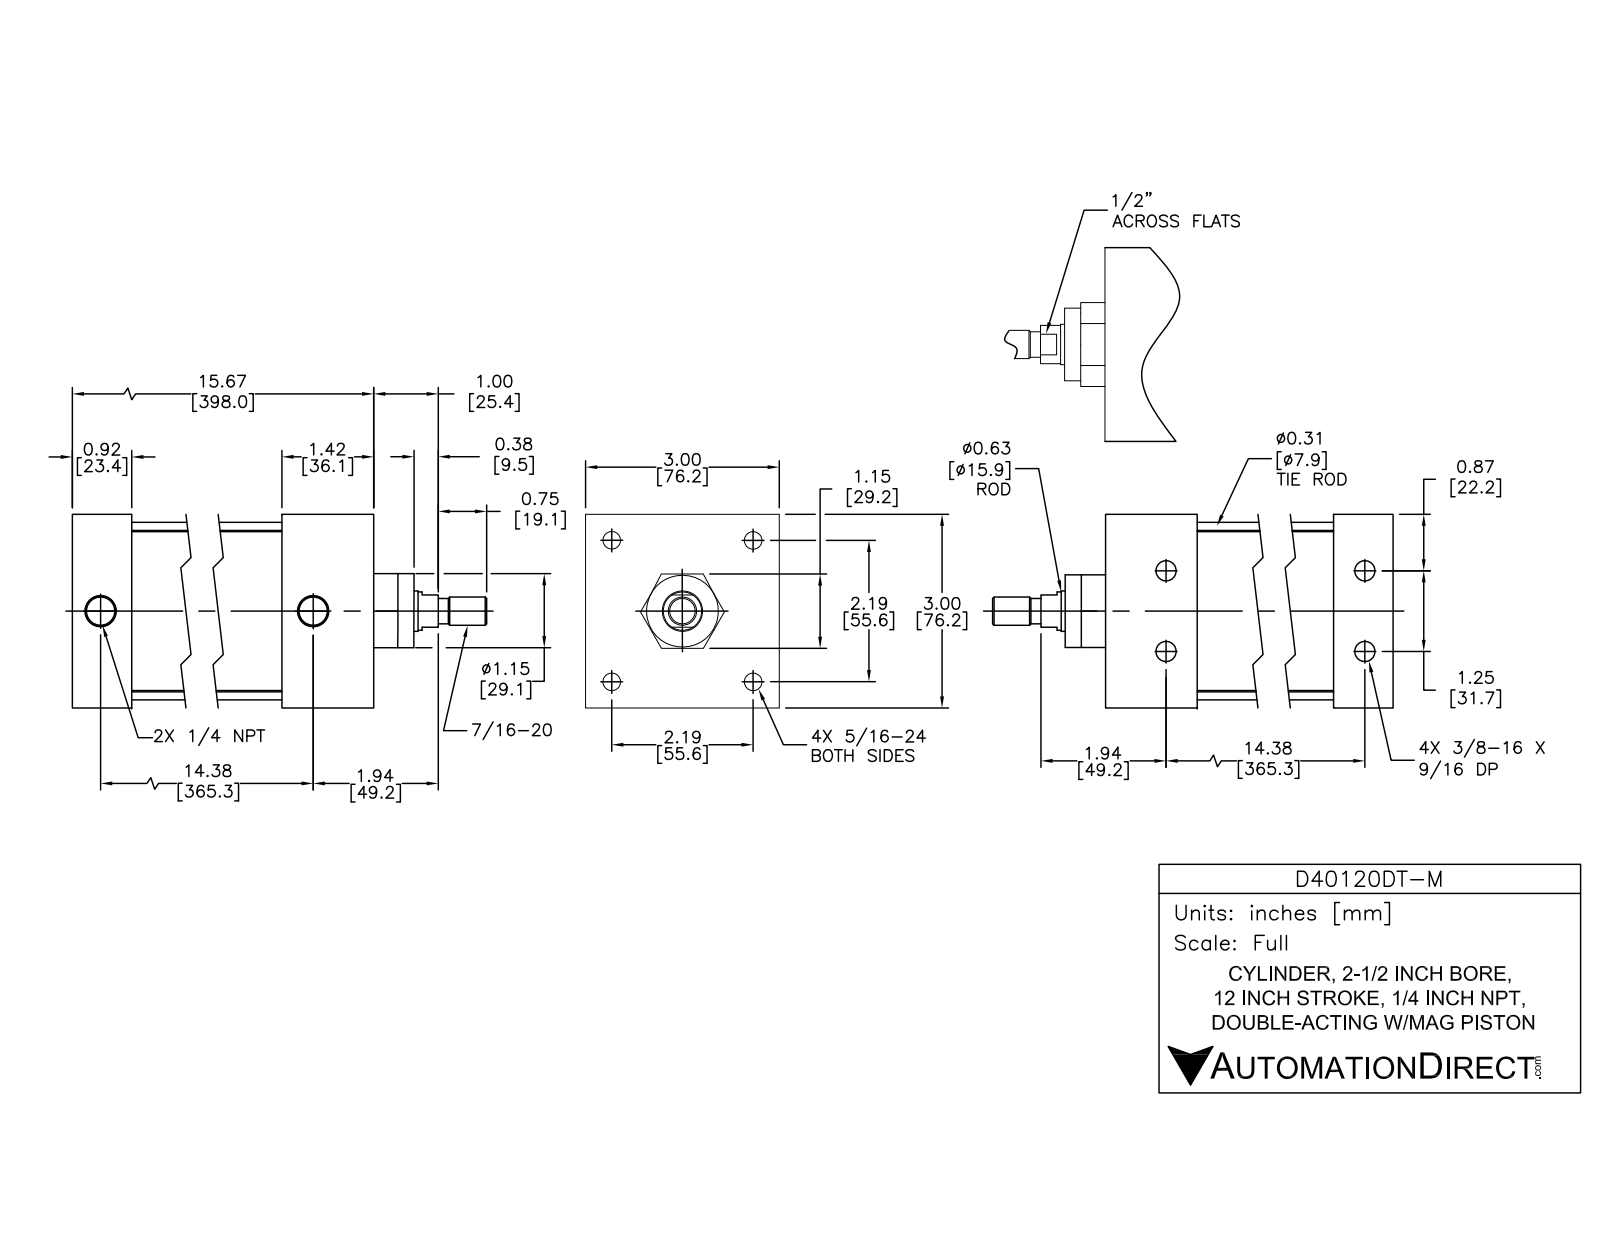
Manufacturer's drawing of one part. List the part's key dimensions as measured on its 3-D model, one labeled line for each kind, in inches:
Part name (STEP PRODUCT): D40120DT-M; D40120DT-M BODY; D40120DT-M PISTON
STEP written by: SolidWorks 2015 (AUTOMOTIVE_DESIGN)
Units: inches
Bodies: 12 solids, 298 faces (94 planar, 114 cylindrical, 90 other)
Overall size (bounding box): 17.496 × 3 × 3
Volume: 48.23 in³ · Surface area: 416.6 in²
Round holes (diameter × count): ⌀0.267 ×4, ⌀0.307 ×4, ⌀0.359 ×4, ⌀0.5 ×4, ⌀0.297 ×2, ⌀0.477 ×2, ⌀0.625 ×1, ⌀0.628 ×1, ⌀2.5 ×1
Round bosses / shafts (diameter × count): ⌀0.484 ×4, ⌀0.313 ×4, ⌀0.282 ×4, ⌀2.75 ×1, ⌀2.497 ×1, ⌀1.12 ×1, ⌀0.622 ×1, ⌀0.59 ×1
Partial cylindrical surfaces — rounded edges, fillets, slot ends (radius × count): R0.3 ×4
Main face-to-face distances: 3, 0.08, 13.326, 15.746, 14.726, 1.02, 1.42, 13.306, 14.326, 1
Hole centre spacings: 1.556, 2.2, 14.37, 0.625, 0.625, 1.25, 3.111, 14.383
